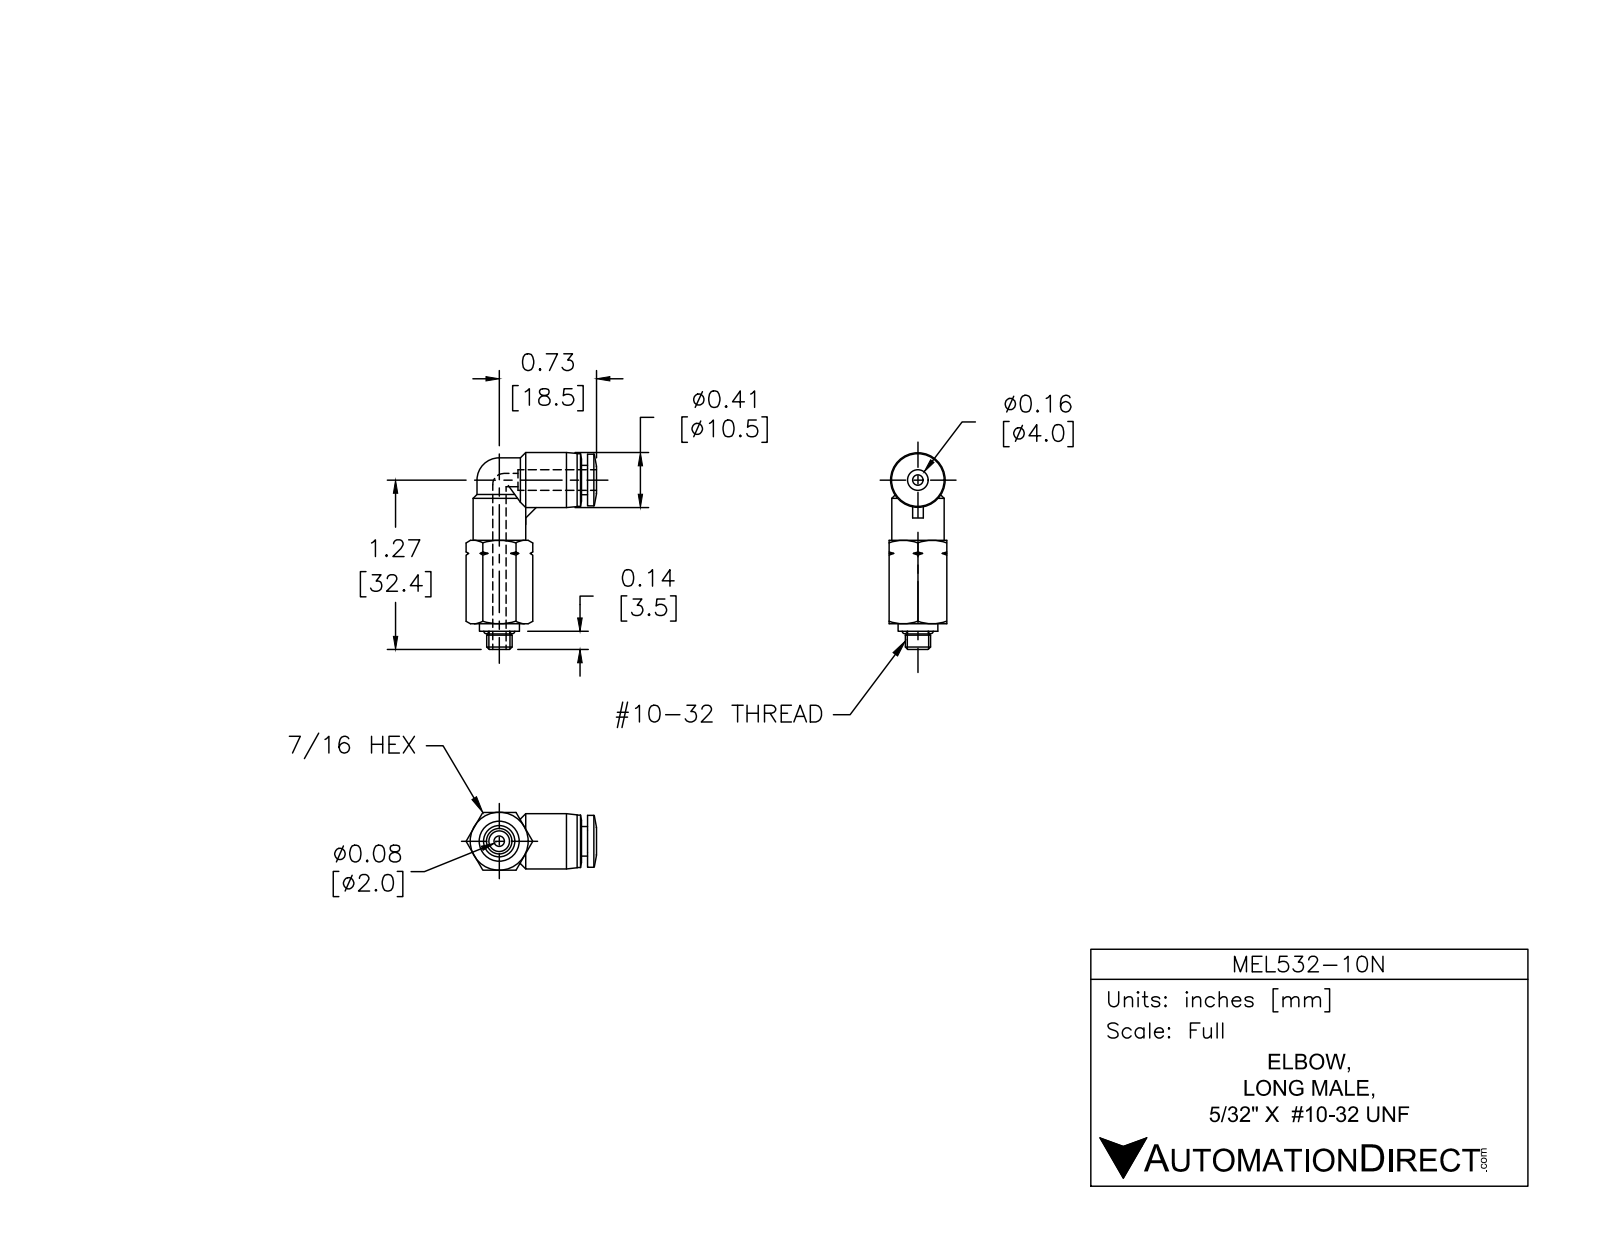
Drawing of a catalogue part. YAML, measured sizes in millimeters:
part_name: "MEL532-10N"
step_written_by: "SolidWorks 2015 (AUTOMOTIVE_DESIGN)"
units: millimeters
bodies: {solids: 2, faces: 105, planar: 18, cylindrical: 29, other: 58}
overall_size: [37.7, 24.8, 11]
volume: 3640
surface_area: 2378
round_holes:
  - {diameter: 2, count: 2}
  - {diameter: 4, count: 1}
  - {diameter: 4.3, count: 1}
round_bosses_or_shafts:
  - {diameter: 10, count: 2}
  - {diameter: 10.5, count: 1}
  - {diameter: 9.9, count: 1}
  - {diameter: 7.6, count: 1}
  - {diameter: 5.6, count: 1}
  - {diameter: 4.8, count: 1}
partial_cylinders:
  - {radius: 4.2, count: 2}
face_to_face_distances: [11, 1.1, 16, 0.6, 16.6, 12, 13.2, 0.8, 1.4, 17.4]
